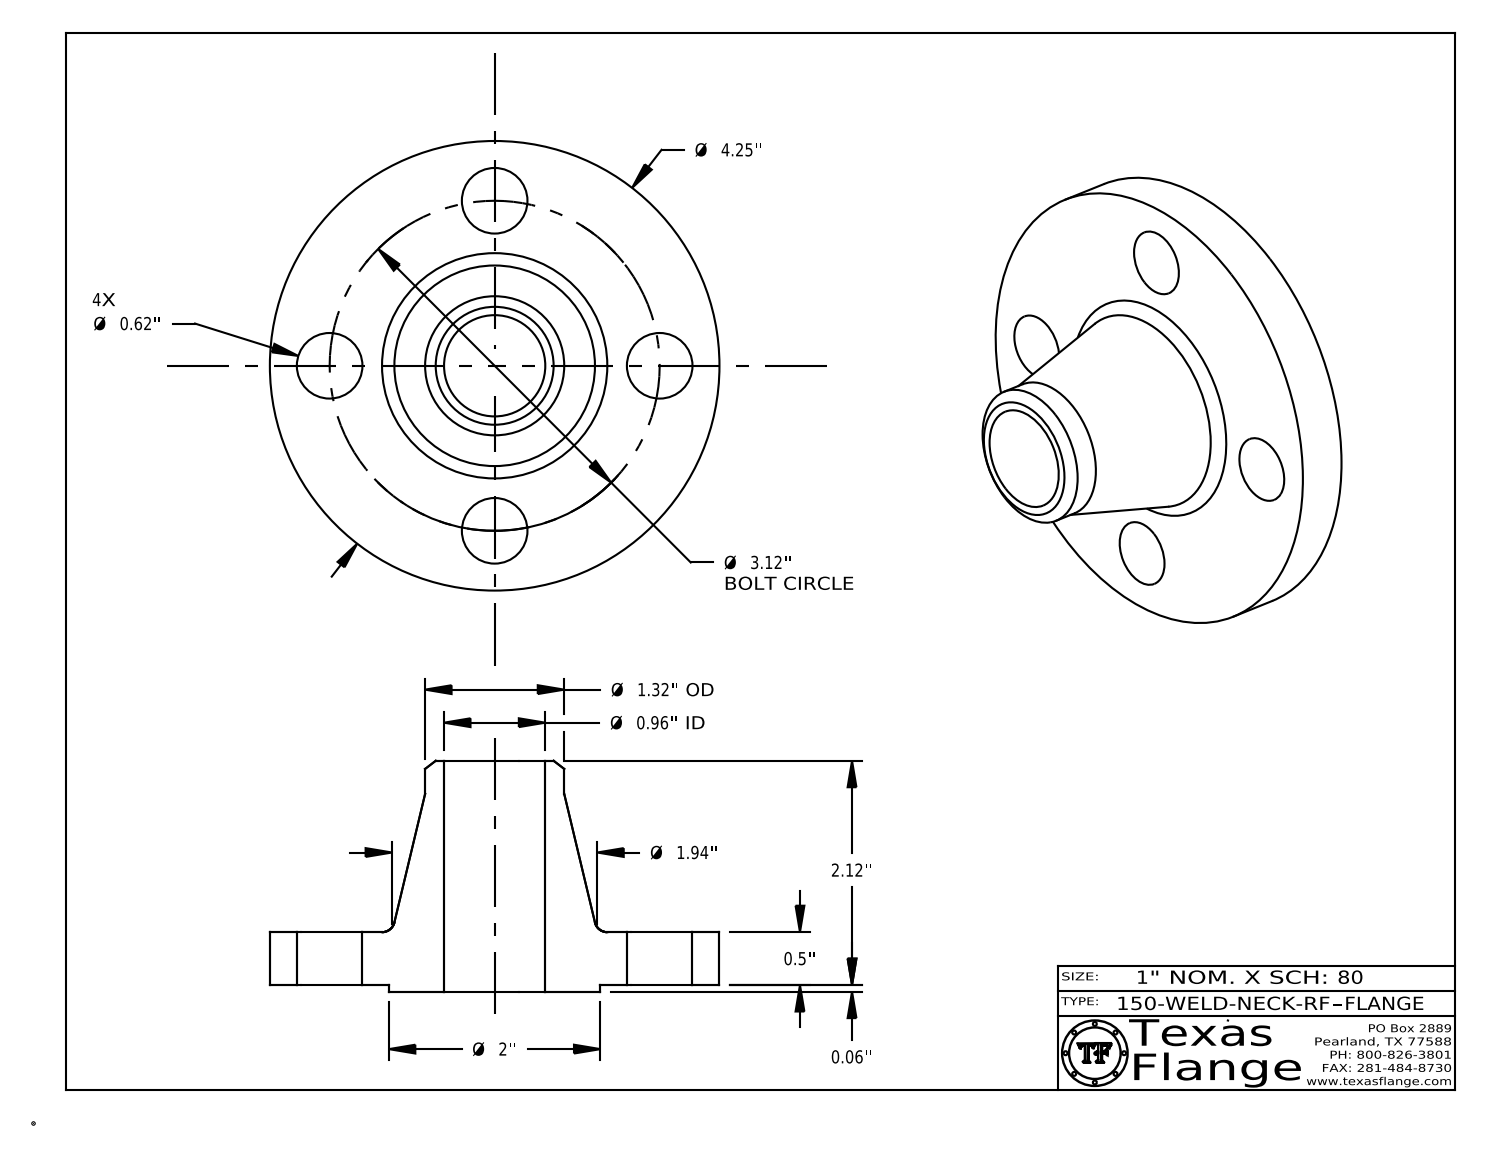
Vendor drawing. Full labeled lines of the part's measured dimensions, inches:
Part name (STEP PRODUCT): 150-WELD-NECK-RF
STEP written by: CATIA V5 STEP AP214 (AUTOMOTIVE_DESIGN)
Units: inches
Bodies: 1 solid, 411 faces (369 planar, 36 cylindrical, 6 other)
Overall size (bounding box): 4.25 × 4.25 × 2.183
Volume: 8.288 in³ · Surface area: 48.31 in²
Round holes (diameter × count): ⌀0.62 ×4, ⌀0.495 ×1, ⌀0.957 ×1
Round bosses / shafts (diameter × count): ⌀0.03 ×8, ⌀4.25 ×1, ⌀2 ×1, ⌀1.315 ×1, ⌀0.39 ×1
Main face-to-face distances: 0.5, 0.063, 0.563, 2.183, 2.12, 1.62, 0.548, 0.485, 0.015, 1.635
Hole centre spacings: 1.56, 2.206, 1.194, 2.882, 3.12, 1.56
